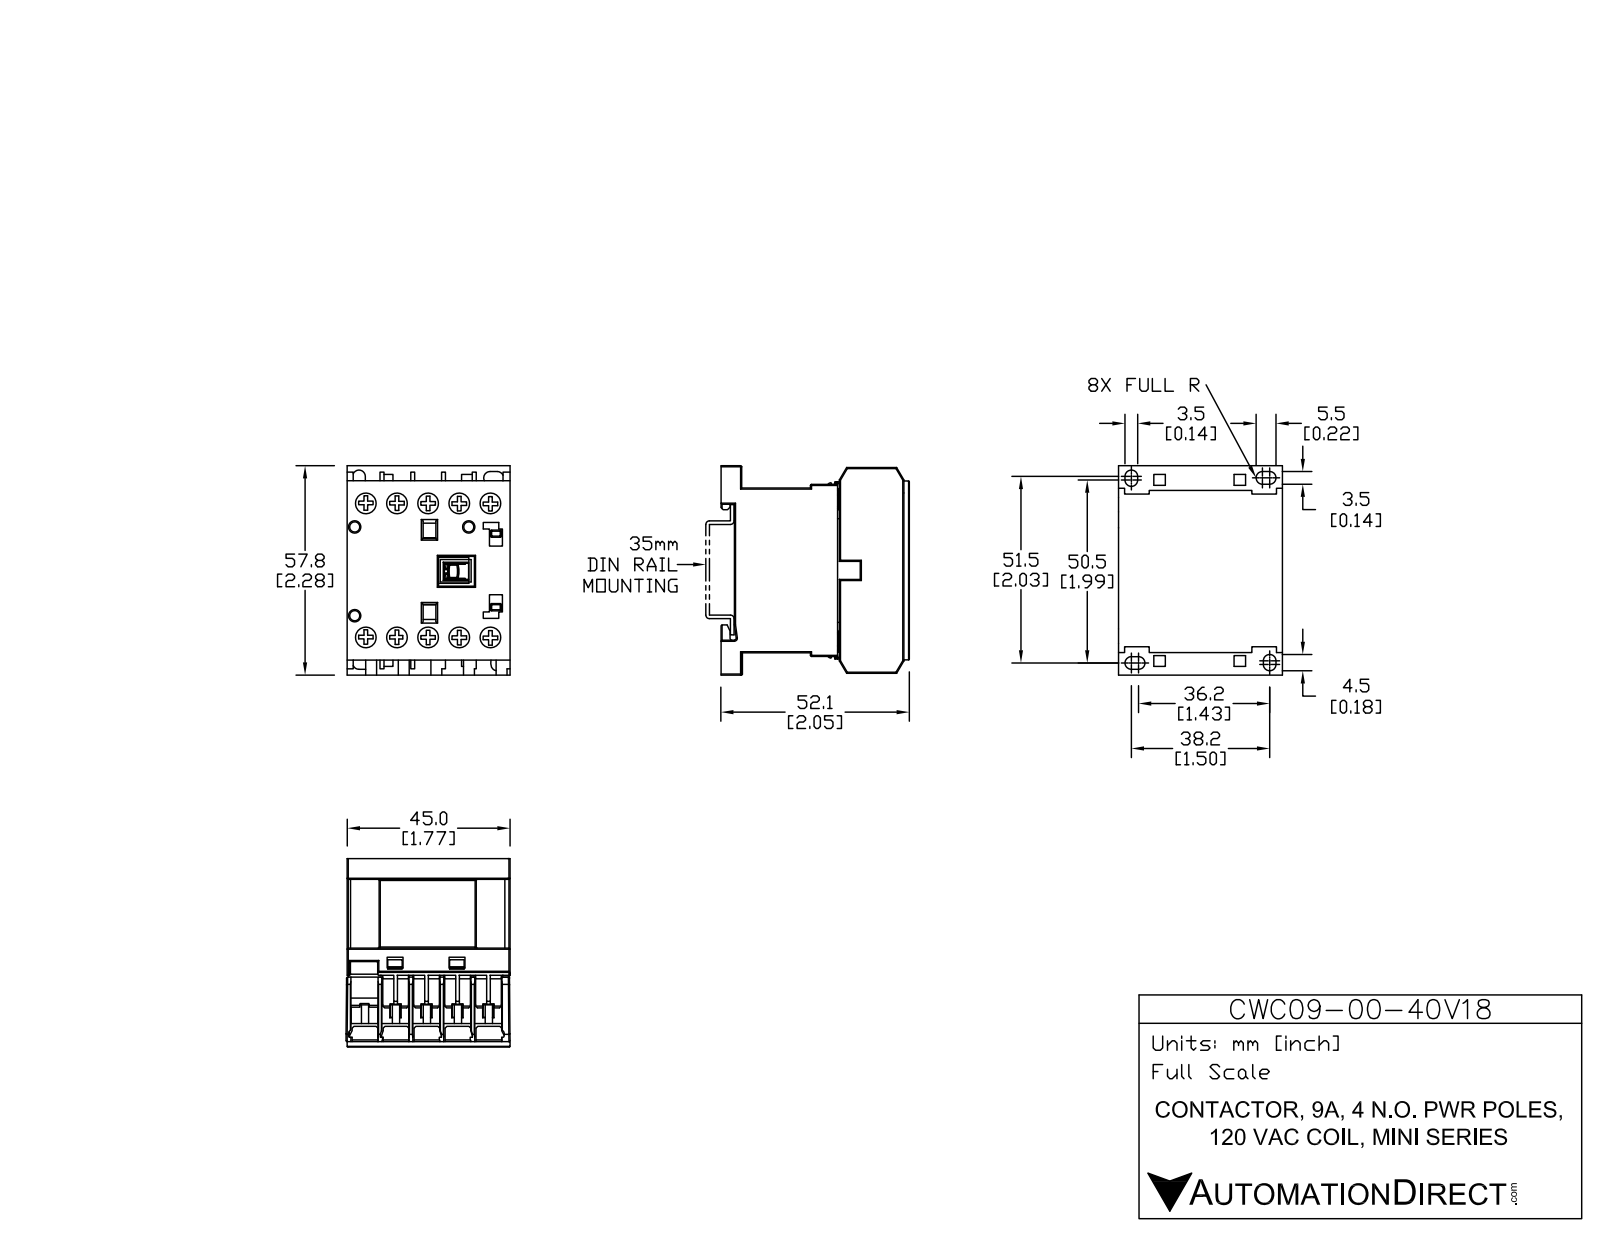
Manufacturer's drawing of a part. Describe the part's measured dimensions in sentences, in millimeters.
The part is named "CWC09-00-40V18". Its 3-D file was written by "SolidWorks 2013 (AUTOMOTIVE_DESIGN)". It is 15 solids with 535 faces: 445 planar, 90 cylindrical and 0 other. Overall it measures 58.04 by 52.12 by 45.75 millimeters. Its volume is 97 133 cubic millimeters and its surface area 30 437 square millimeters. Round holes: 10 of diameter 6.2, 3 of diameter 2.8. Round bosses or shafts: 10 of diameter 5.9. Partial cylindrical surfaces (rounded edges, fillets, slot ends): 20 of radius 0.3, 6 of radius 1.72, 2 of radius 1.73, 1 of radius 0.32, 1 of radius 0.42, 1 of radius 0.55. The main face-to-face distances are 8.25, 45.5, 1.25, 16.5, 9.5, 5.5, 17.75, 5.13, 10.63, 7. The hole center spacings are 8.55, 37.94, 17.1, 40.72, 36.96, 25.65, 44.99, 6.91.
